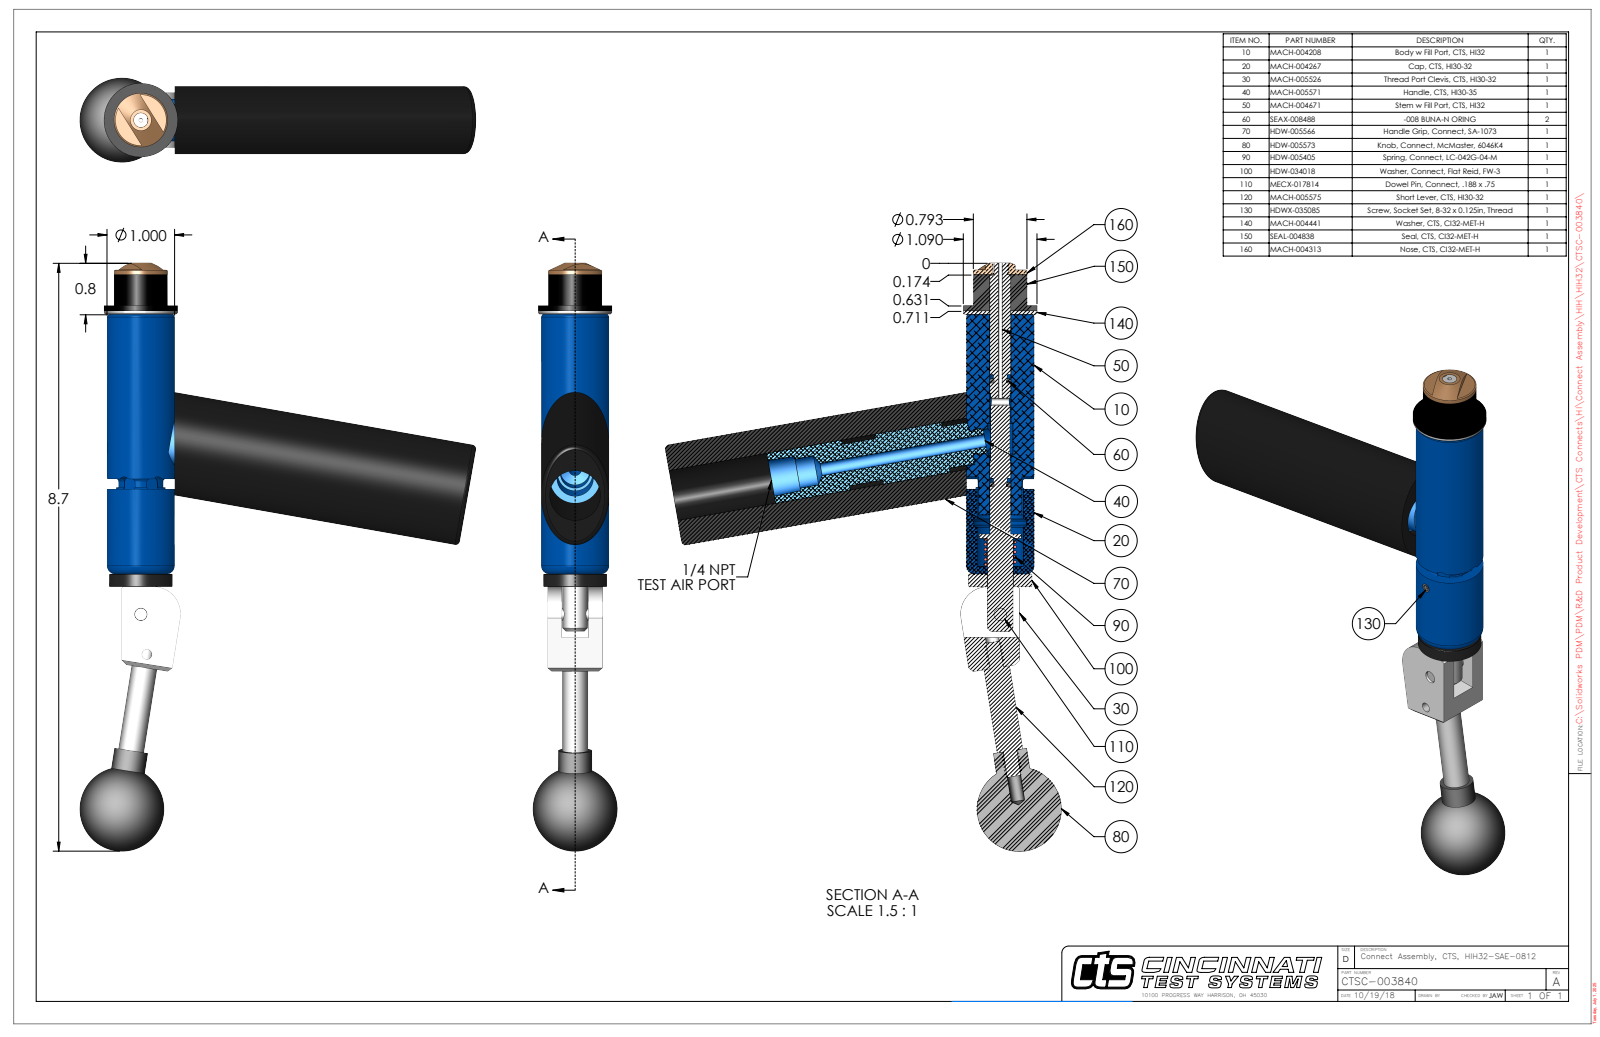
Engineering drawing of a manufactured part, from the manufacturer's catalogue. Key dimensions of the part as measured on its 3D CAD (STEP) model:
Part name (STEP PRODUCT): CTSC-003840
STEP written by: SolidWorks 2023 (AUTOMOTIVE_DESIGN)
Units: inches
Bodies: 10 solids, 320 faces (122 planar, 126 cylindrical, 72 other)
Overall size (bounding box): 8.692 × 5.856 × 1.25
Volume: 9.539 in³ · Surface area: 79.44 in²
Round holes (diameter × count): ⌀0.201 ×2, ⌀0.063 ×1, ⌀0.109 ×1, ⌀0.136 ×1, ⌀0.15 ×1, ⌀0.187 ×1, ⌀0.189 ×1, ⌀0.213 ×1, ⌀0.31 ×1, ⌀0.314 ×1, ⌀0.316 ×1, ⌀0.385 ×1
Round bosses / shafts (diameter × count): ⌀0.25 ×2, ⌀0.201 ×2, ⌀1.09 ×1, ⌀1 ×1, ⌀0.936 ×1, ⌀0.793 ×1, ⌀0.75 ×1, ⌀0.62 ×1
Partial cylindrical surfaces — rounded edges, fillets, slot ends (radius × count): R0.093 ×6, R0.029 ×2, R0.065 ×1, R0.325 ×1, R0.375 ×1, R0.4 ×1, R0.452 ×1
Main face-to-face distances: 0.05, 0.21, 0.602, 0.537, 0.587, 4.42, 3.883, 3.833, 0.812, 4.608
Hole centre spacings: 0.599, 1.658, 2.252
